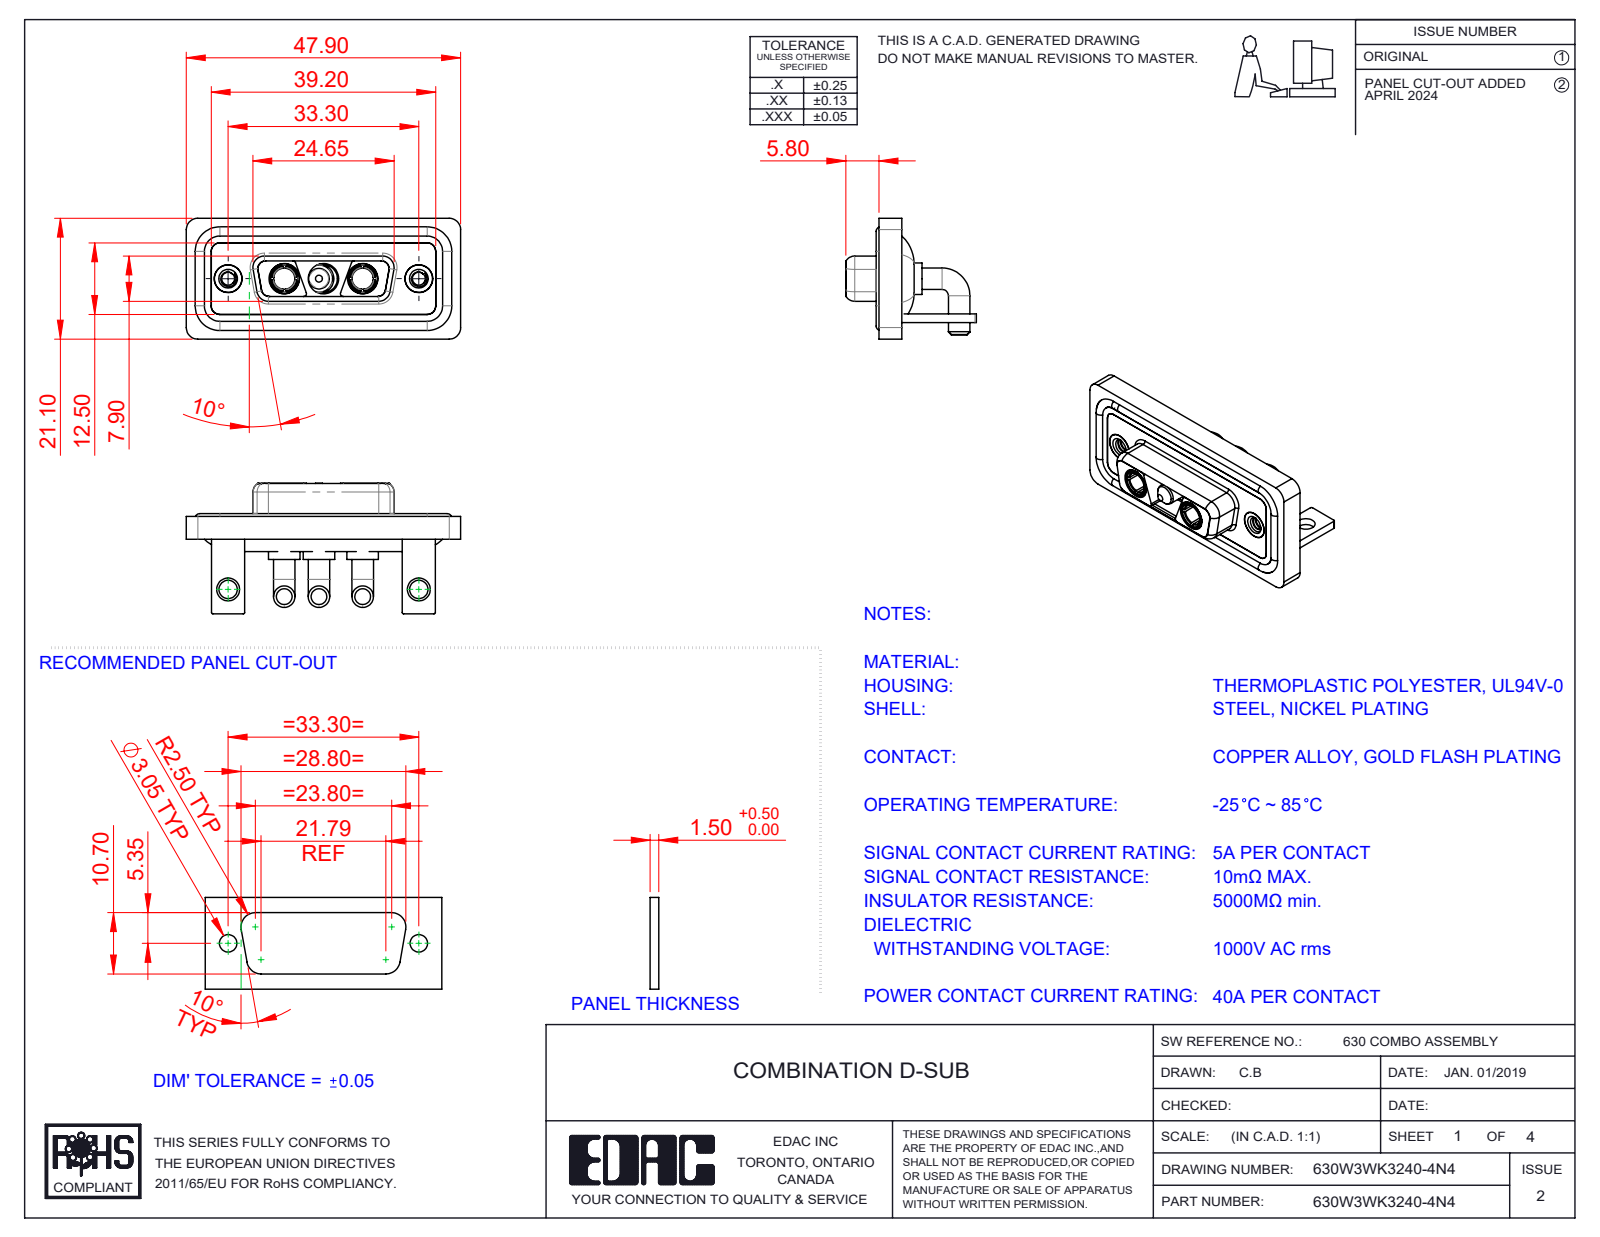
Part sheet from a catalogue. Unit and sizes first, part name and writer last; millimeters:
Units: millimetres
Overall size (bounding box): 47.9 × 22.8 × 21.1
Round holes (diameter × count): ⌀4.85 ×5, ⌀5.3 ×3, ⌀2.26 ×2, ⌀3.2 ×2, ⌀3.7 ×2, ⌀4 ×2, ⌀4.05 ×2, ⌀5 ×2
Round bosses / shafts (diameter × count): ⌀3.75 ×6, ⌀1.6 ×4, ⌀5.5 ×3, ⌀5.2 ×3, ⌀4.75 ×3, ⌀4.96 ×2, ⌀4.95 ×2, ⌀4.8 ×2
Partial cylindrical surfaces — rounded edges, fillets, slot ends (radius × count): R2 ×21, R1.5 ×18, R0.25 ×16, R1.35 ×12, R0.5 ×9, R1.6 ×8, R0.6 ×4, R0.65 ×4
Main face-to-face distances: 0.4, 2.9, 1.5, 3.7, 1.8, 1.1, 4.1, 1.6, 2.5, 1.4
Hole centre spacings: 6.85, 9.8, 16.65, 23.5, 33.3, 13.7
Volume: 6 617 mm³ · Surface area: 10 605 mm²
Bodies: 15 solids, 643 faces (198 planar, 288 cylindrical, 157 other)
Part name (STEP PRODUCT): 630Combo Stabilizer Bracket_50 Contacts; 630W3WK3140-4N4; 630Combo Threaded Rivet_2; Power Socket_40A RA (+5 more)
STEP written by: SolidWorks 2023 (CONFIG_CONTROL_DESIGN)
